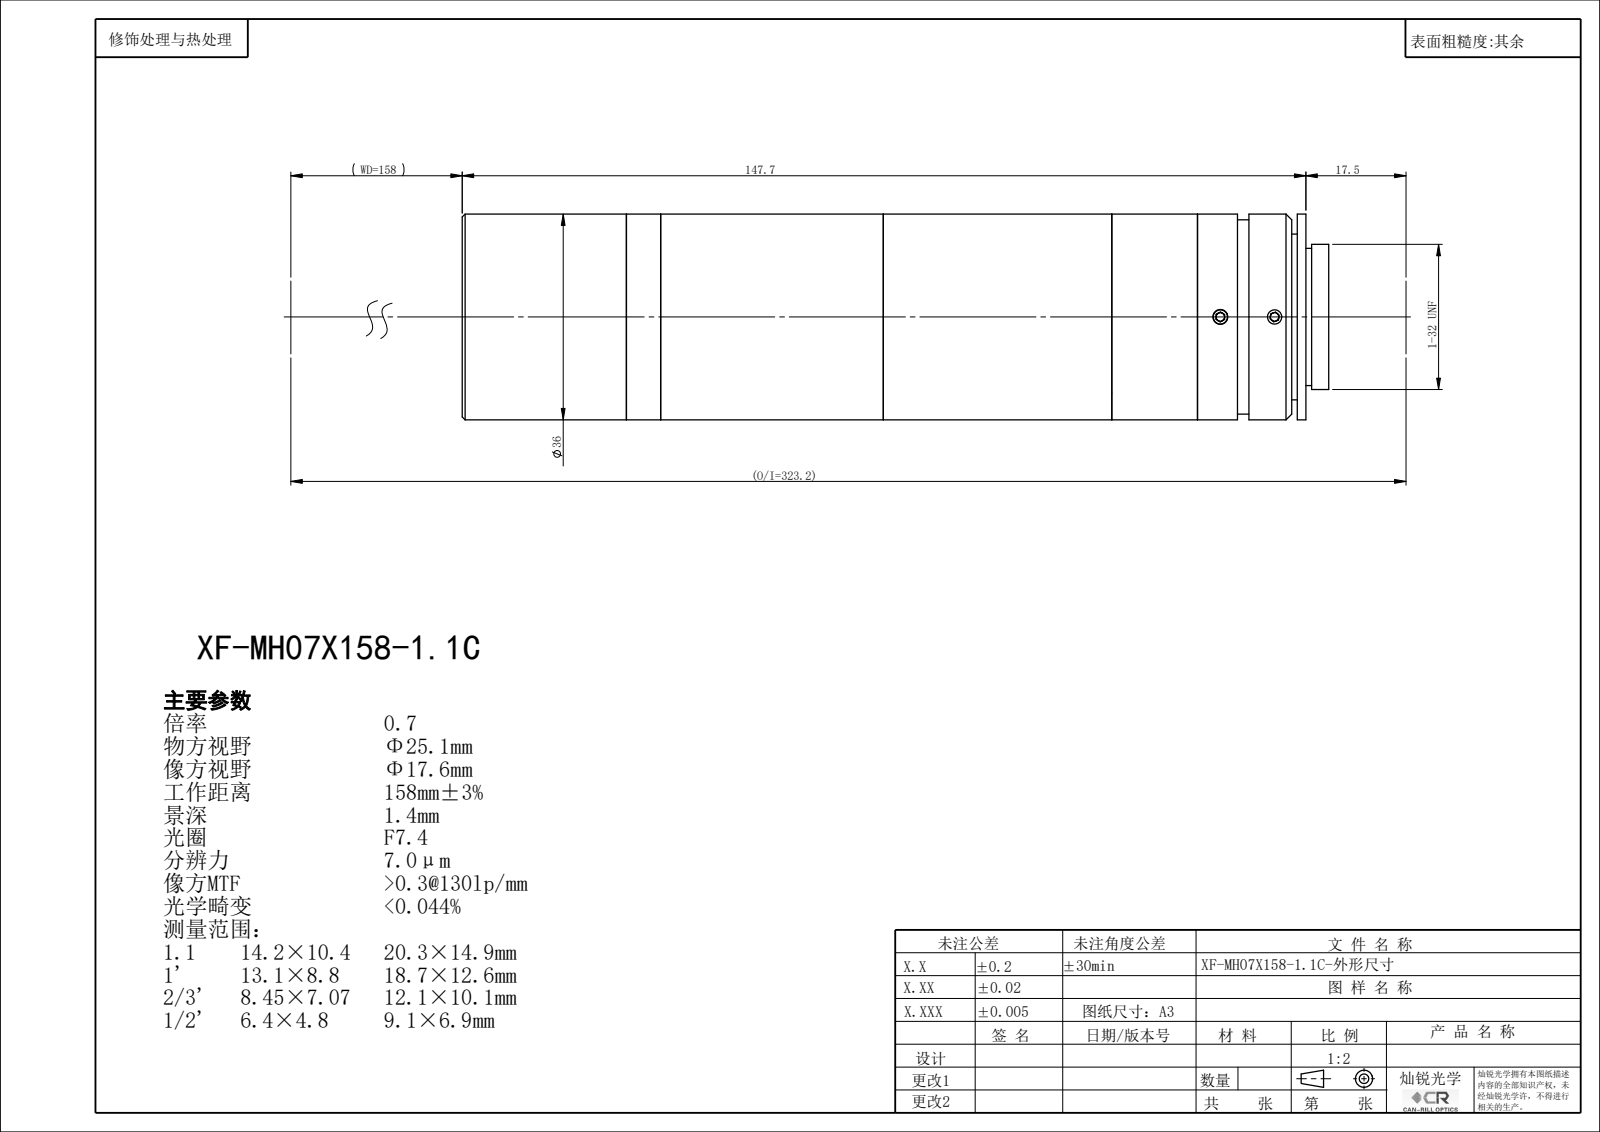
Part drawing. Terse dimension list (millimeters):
name: XF-MH07X158-1.1C
written by: SolidWorks 2022 (CONFIG_CONTROL_DESIGN)
unit: mm
bodies: 0 solids, 132 faces (68 planar, 42 cylindrical, 22 other)
size: 151.69 × 36 × 36
holes: 3× ⌀2.5, 1× ⌀22.4, 1× ⌀24, 1× ⌀26, 1× ⌀26.4, 1× ⌀29.4, 1× ⌀33.4, 1× ⌀34.5
bosses: 1× ⌀36, 1× ⌀34, 1× ⌀25.4
face distances: 18.97, 1.5, 17.47, 15, 32.47, 33.97, 40, 55, 72.47, 73.97
